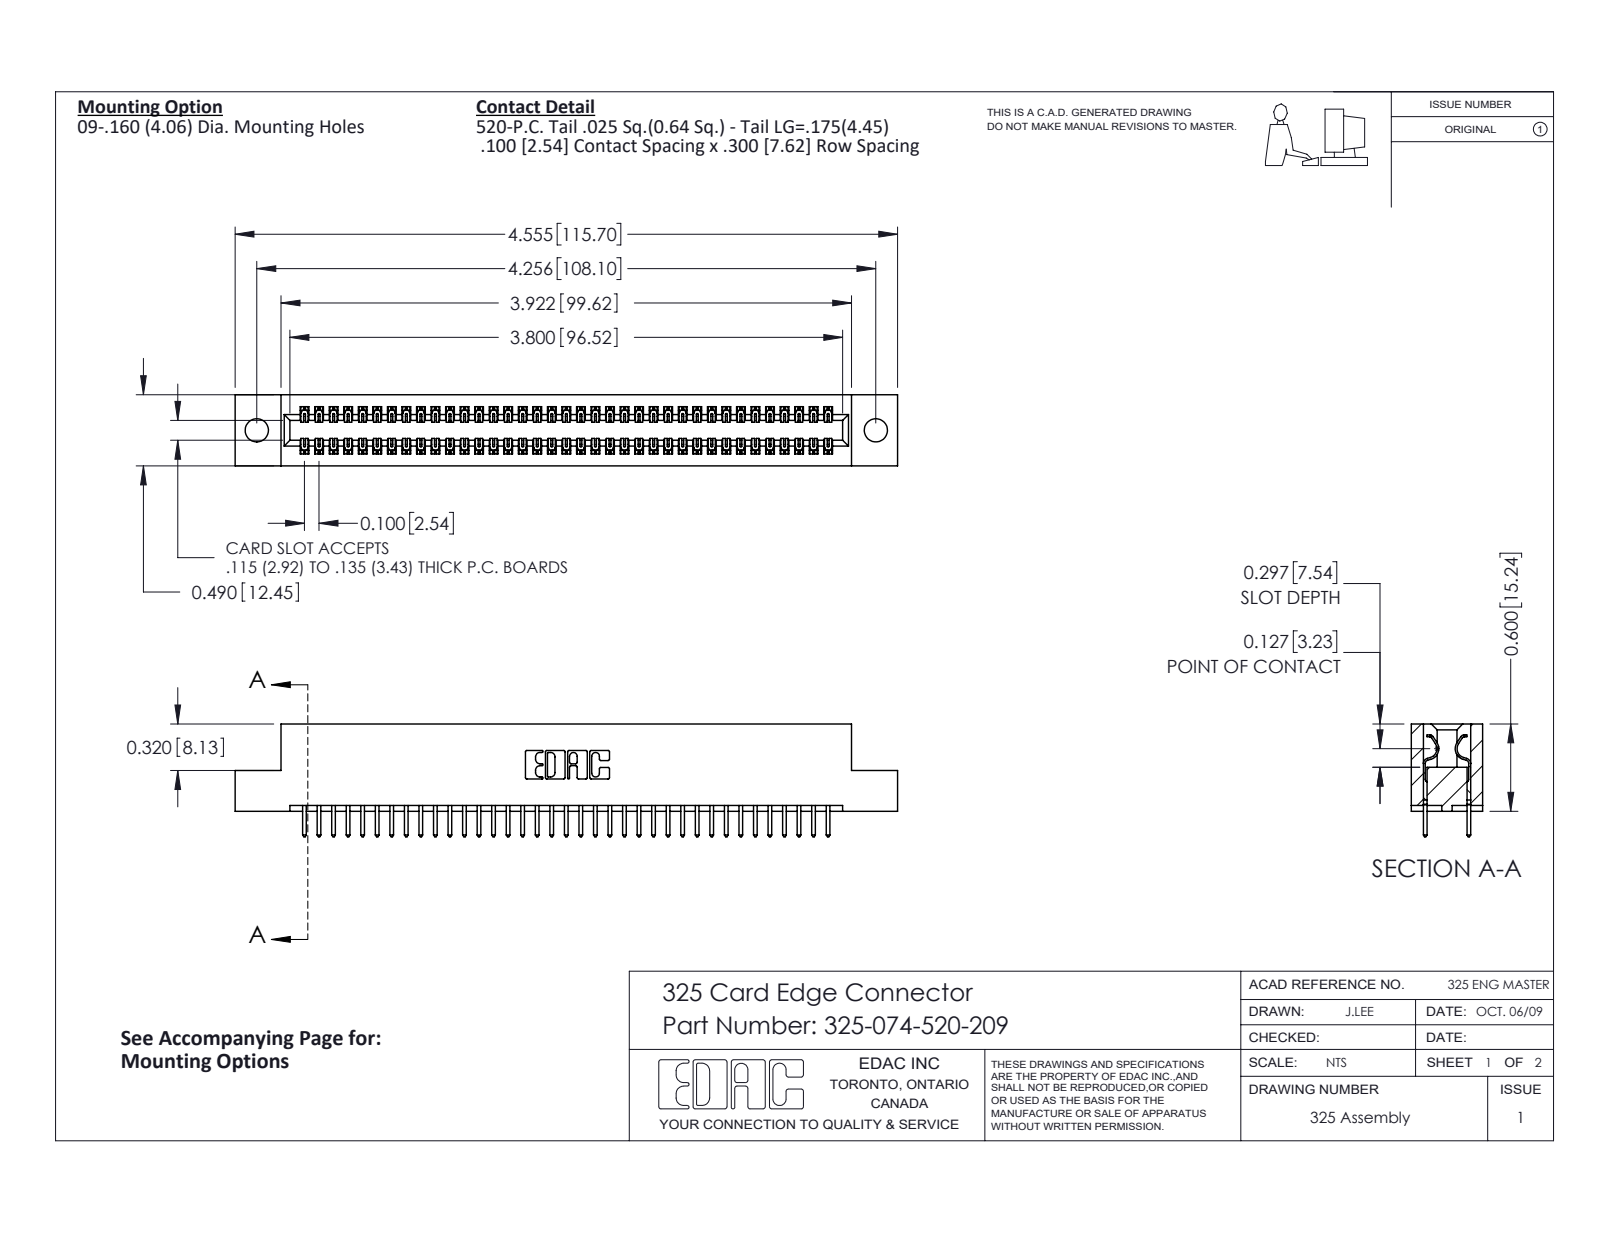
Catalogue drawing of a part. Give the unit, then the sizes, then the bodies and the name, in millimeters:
Units: millimetres
Overall size (bounding box): 115.7 × 19.7 × 12.4
Round holes (diameter × count): ⌀4.1 ×2
Partial cylindrical surfaces — rounded edges, fillets, slot ends (radius × count): R0.2 ×111, R0.3 ×74, R0.3 ×22, R0.2 ×6, R0.8 ×6, R0.7 ×3, R0.4 ×2, R0.6 ×2
Main face-to-face distances: 2.1, 10.3, 12.4, 7.6, 2.7, 9.7, 0.6, 8.3, 7, 14.2
Hole centre spacings: 108.1
Volume: 14 700 mm³ · Surface area: 17 380 mm²
Bodies: 75 solids, 3962 faces (2734 planar, 1228 cylindrical, 0 other)
Part name (STEP PRODUCT): 325-292-001_325-293-120; 325 Part_.160 TH; 325-074-520-209
STEP written by: SolidWorks 2016 (CONFIG_CONTROL_DESIGN)
